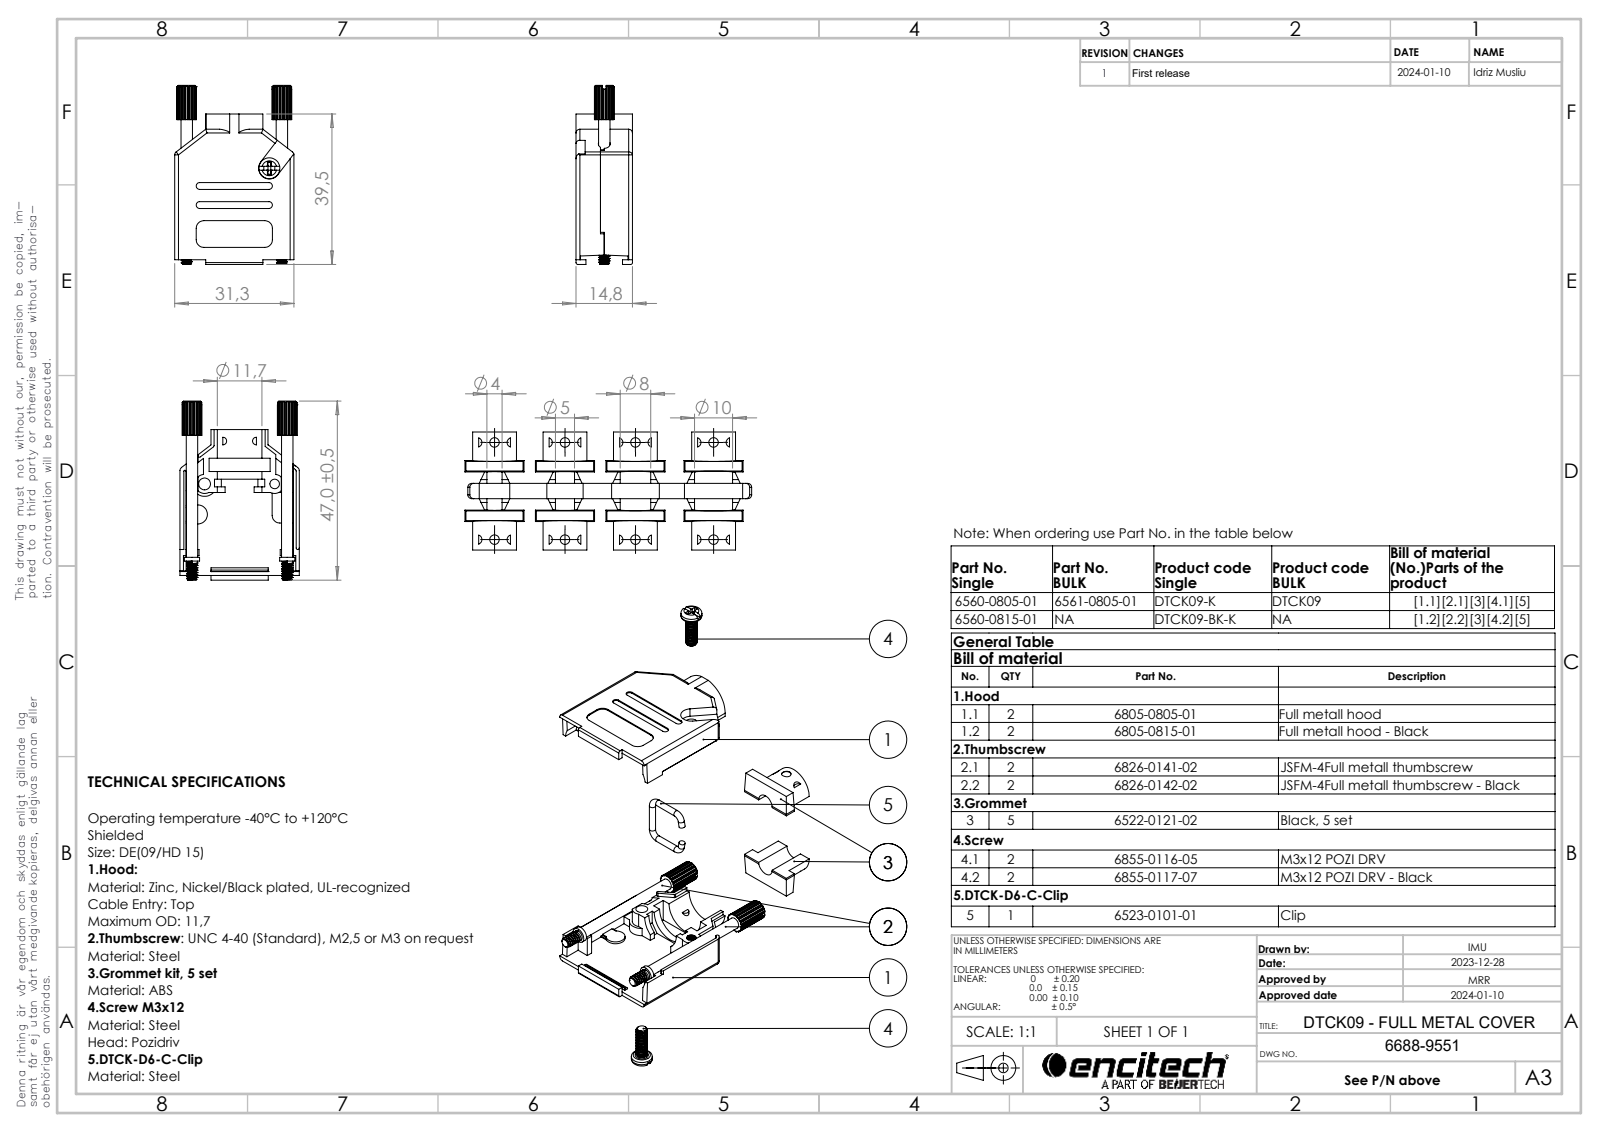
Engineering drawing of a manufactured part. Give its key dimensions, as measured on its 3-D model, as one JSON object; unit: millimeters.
{"part_name": "6855-0116-05; 6522-0121-02 (5mm); 6523-0101-01; 6805-0805-01 (+2 more)", "step_written_by": "SolidWorks 2021 (AUTOMOTIVE_DESIGN)", "units": "millimeters", "bodies": {"solids": 9, "faces": 810, "planar": 408, "cylindrical": 346, "other": 56}, "overall_size": [47, 31.3, 14.8], "volume_mm3": 7299, "surface_area_mm2": 11028, "round_holes": [[3.1, 4], [2.5, 3], [5, 1], [11.7, 1]], "round_bosses_or_shafts": [[1.6, 5], [3, 4], [5.5, 2], [4, 2], [2.85, 2], [15, 1], [11.5, 1]], "partial_cylinders_radius": [[0.25, 22], [1, 14], [0.4, 10], [2, 6], [0.9, 4], [2.5, 4], [5, 4], [0.37, 2]], "face_to_face_distances": [1.15, 13.65, 7.4, 6.25, 1.6, 14.8, 12.5, 29.7, 0.85, 14.5], "hole_center_spacings": [12.5, 14.73, 18.4, 25]}
